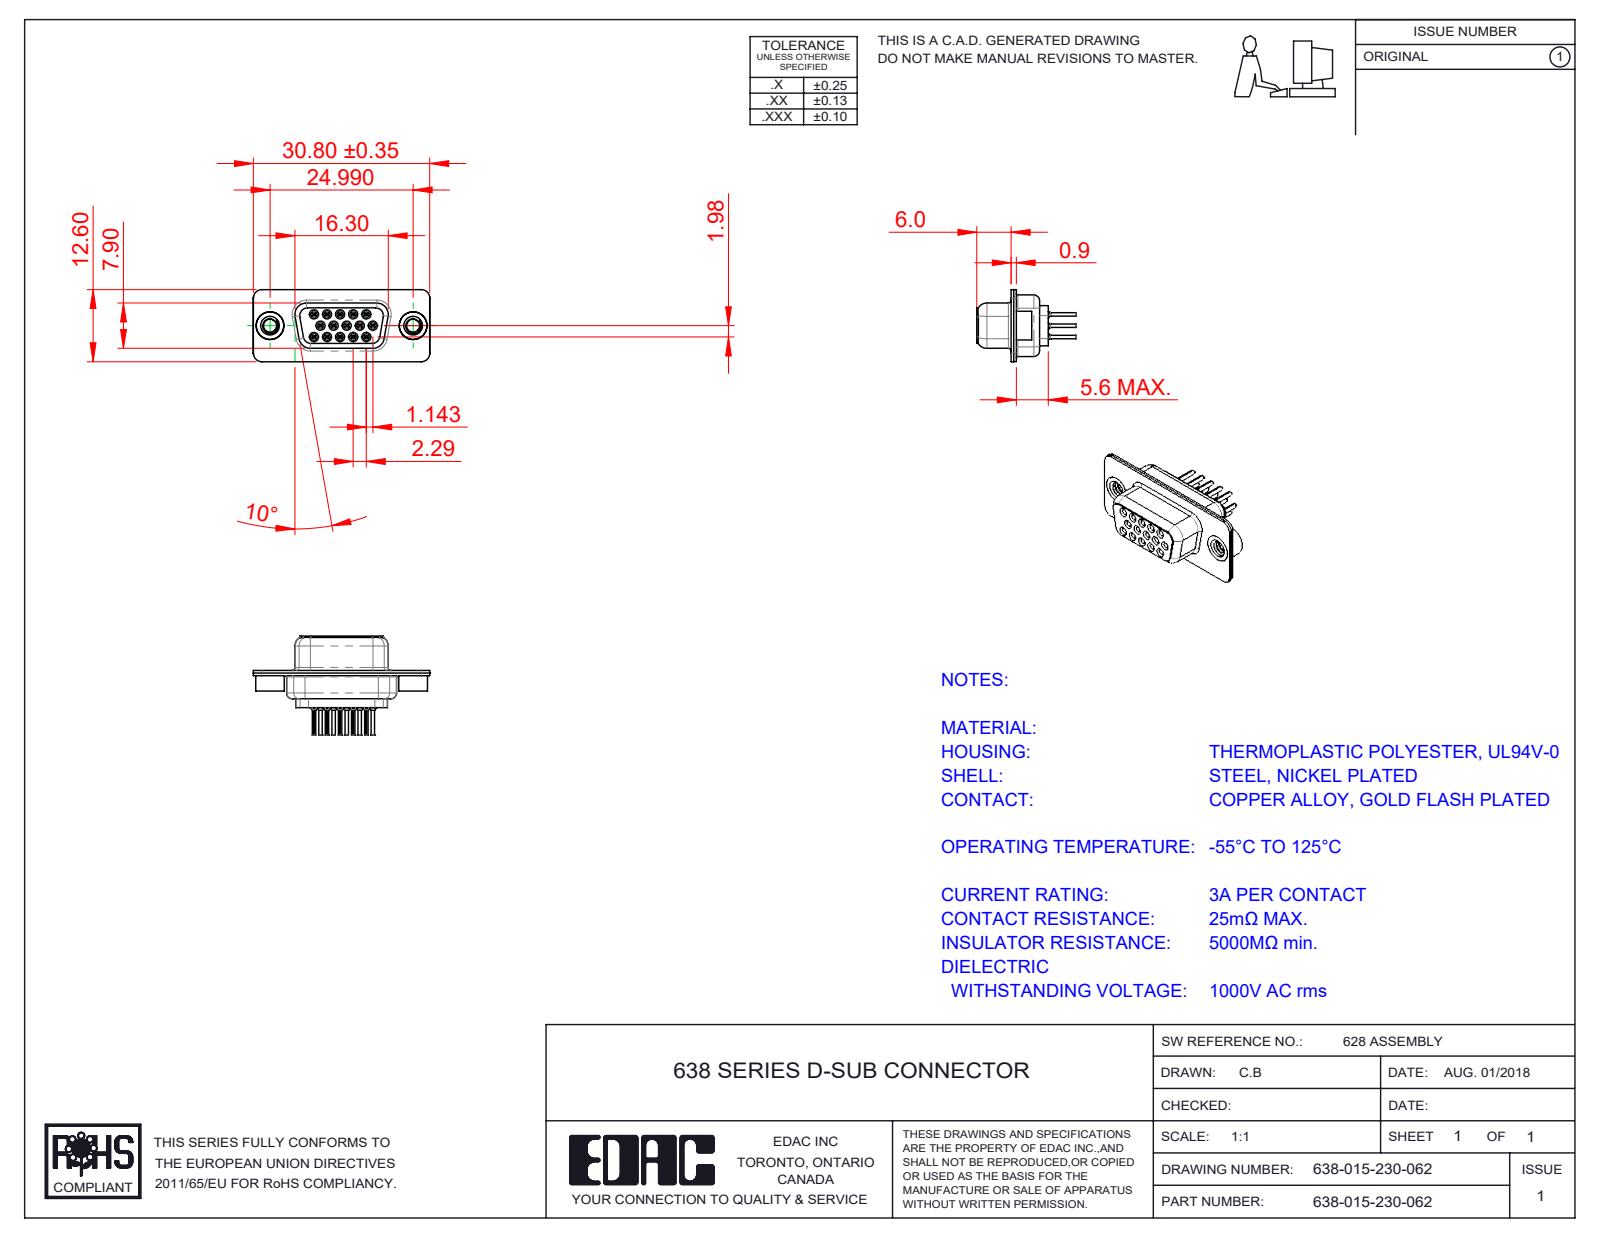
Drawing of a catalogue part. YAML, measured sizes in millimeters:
part_name: "638 Contact Row 1_30; 638 Contact Row 3_30; 638 Housing_15 Contacts; 638 Shell Front_15 Contacts (+4 more)"
step_written_by: "SolidWorks 2020 (CONFIG_CONTROL_DESIGN)"
units: millimeters
bodies: {solids: 20, faces: 2184, planar: 532, cylindrical: 632, other: 1020}
overall_size: [30.81, 17.3, 12.6]
volume: 1577
surface_area: 5598
round_holes:
  - {diameter: 0.2, count: 15}
  - {diameter: 0.8, count: 15}
  - {diameter: 1, count: 15}
  - {diameter: 1.1, count: 15}
  - {diameter: 1.6, count: 15}
  - {diameter: 1.7, count: 15}
  - {diameter: 1.8, count: 15}
  - {diameter: 2, count: 2}
  - {diameter: 2.26, count: 2}
  - {diameter: 4, count: 2}
  - {diameter: 4.05, count: 2}
  - {diameter: 4.85, count: 2}
round_bosses_or_shafts:
  - {diameter: 2, count: 15}
  - {diameter: 1.5, count: 15}
  - {diameter: 1.2, count: 15}
  - {diameter: 0.6, count: 15}
  - {diameter: 5, count: 2}
  - {diameter: 4.95, count: 2}
  - {diameter: 4.8, count: 2}
partial_cylinders:
  - {radius: 0.1, count: 30}
  - {radius: 1.5, count: 20}
  - {radius: 2, count: 12}
  - {radius: 0.28, count: 10}
  - {radius: 1.55, count: 8}
  - {radius: 1.35, count: 5}
  - {radius: 0.25, count: 4}
  - {radius: 0.5, count: 4}
face_to_face_distances: [0.45, 0.9, 0.4, 1.43, 8.88, 6.6, 1.4, 2.28, 0.85, 7.05]
hole_center_spacings: [3.96, 2.28, 4.57, 2.29, 6.05, 6.04, 6.86, 7.92]
